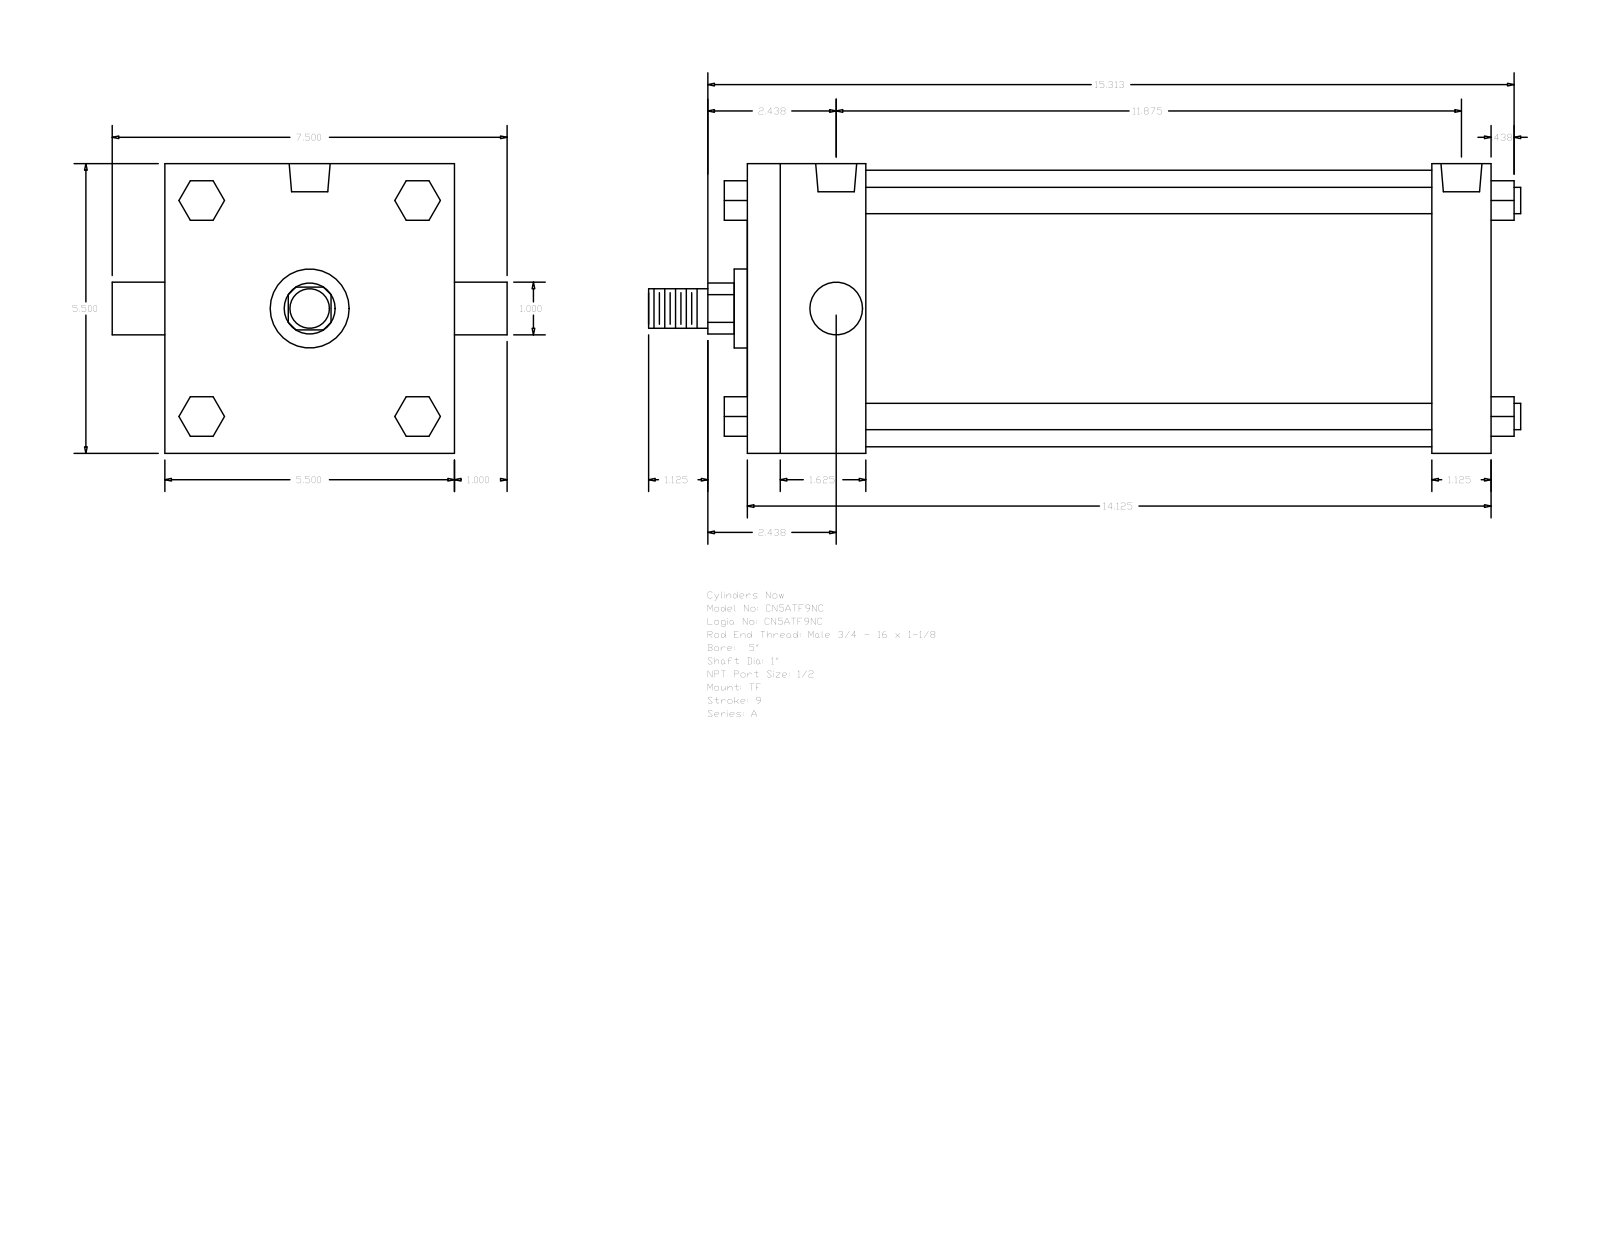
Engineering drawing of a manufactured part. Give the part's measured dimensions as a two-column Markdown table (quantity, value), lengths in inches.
| quantity | value |
| --- | --- |
| part name | A_TF__0500_1 |
| STEP written by | GSSL Pune (CONFIG_CONTROL_DESIGN) |
| units | inches |
| bodies | 0 solids, 120 faces (92 planar, 28 cylindrical, 0 other) |
| overall size | 16.563 × 7.5 × 5.5 |
| round holes (diameter × count) | 0.344 × 3, 0.778 × 2 |
| round bosses / shafts (diameter × count) | 0.5 × 4, 1 × 2, 5.25 × 1, 1.5 × 1, 0.75 × 1 |
| partial cylindrical surfaces (radius × count) | 0.484 × 1 |
| main face-to-face distances | 5.5, 14.125, 1.125, 13, 2.25, 10.75, 11.875, 0.75, 2.05, 3.55 |
| hole center spacings | 0.094, 11.781, 11.687, 11.875 |
